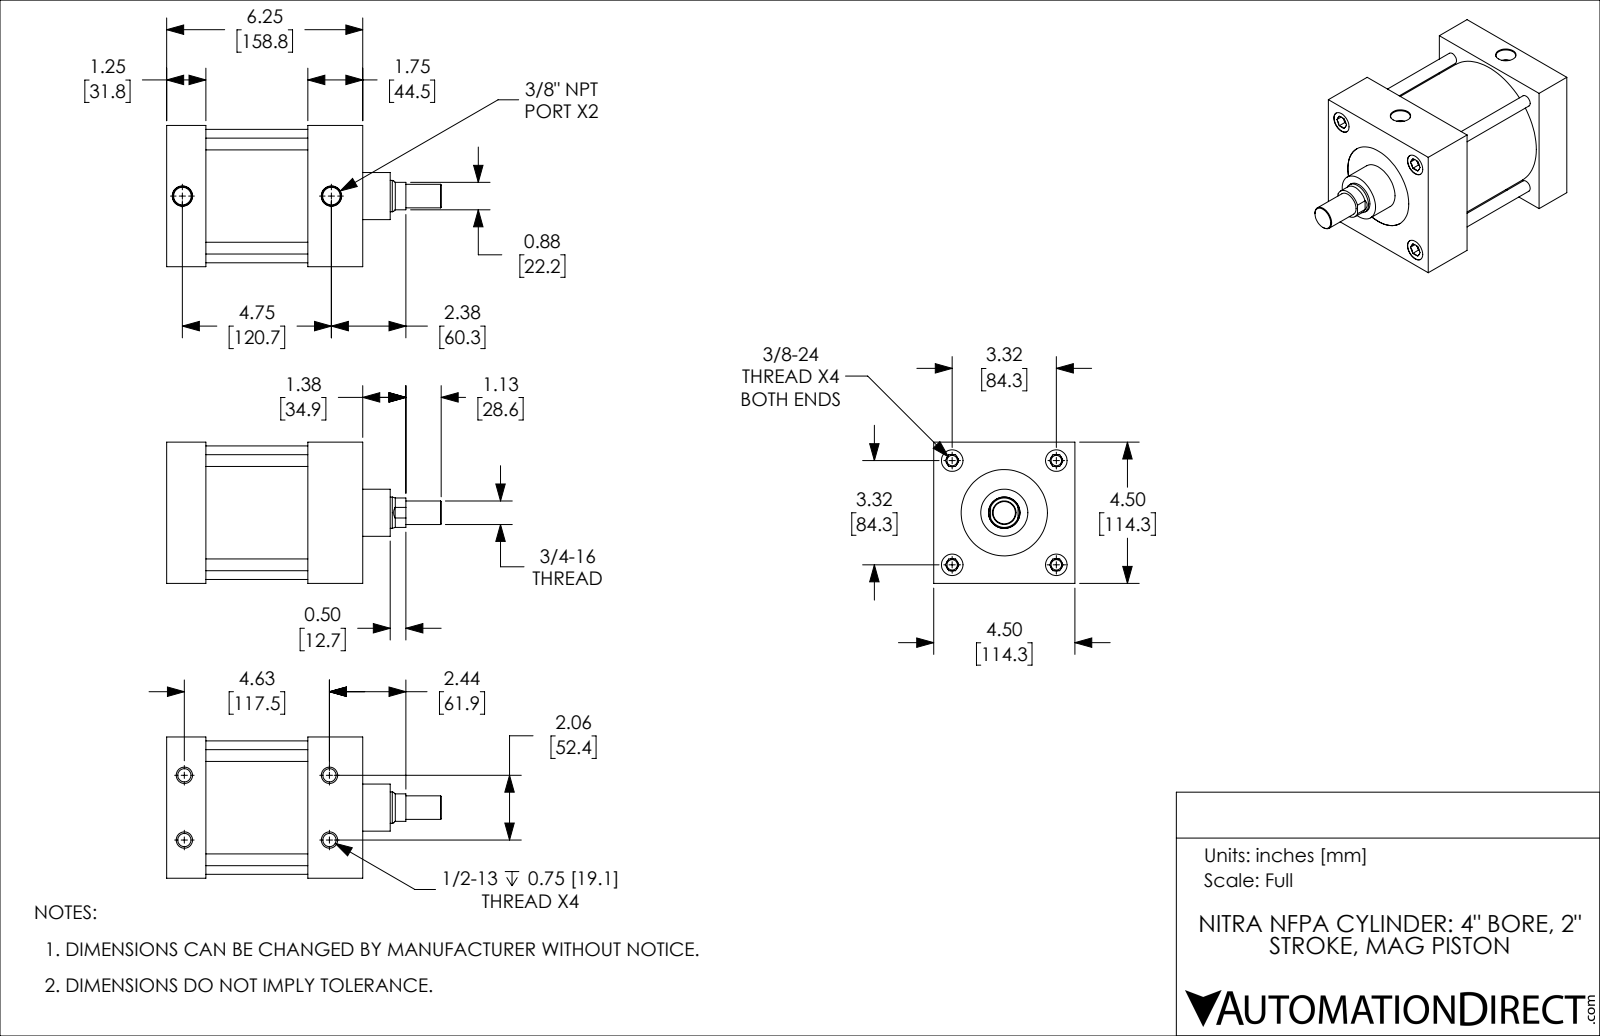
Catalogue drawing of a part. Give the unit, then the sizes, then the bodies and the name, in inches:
Units: inches
Overall size (bounding box): 8.75 × 4.5 × 4.5
Round holes (diameter × count): ⌀0.332 ×4, ⌀0.422 ×4, ⌀0.687 ×4, ⌀0.562 ×2, ⌀1.001 ×1, ⌀2.75 ×1, ⌀4.001 ×1
Round bosses / shafts (diameter × count): ⌀0.375 ×4, ⌀4.251 ×1, ⌀3.999 ×1, ⌀1.5 ×1, ⌀0.999 ×1, ⌀0.75 ×1
Partial cylindrical surfaces — rounded edges, fillets, slot ends (radius × count): R0.469 ×1
Main face-to-face distances: 4.5, 1.25, 3.25, 6.25, 5, 1.75, 2.5, 2, 3.75, 6.245
Hole centre spacings: 2.347, 3.32, 4.8, 1.033, 4.625, 4.695, 1.034, 2.062
Volume: 84.73 in³ · Surface area: 320.6 in²
Bodies: 2 solids, 198 faces (58 planar, 62 cylindrical, 78 other)
Part name (STEP PRODUCT): D264020DT-M_PISTON_KK1; D264020DT-M; D264020DT-M_BODY
STEP written by: SolidWorks 2019 (CONFIG_CONTROL_DESIGN)
